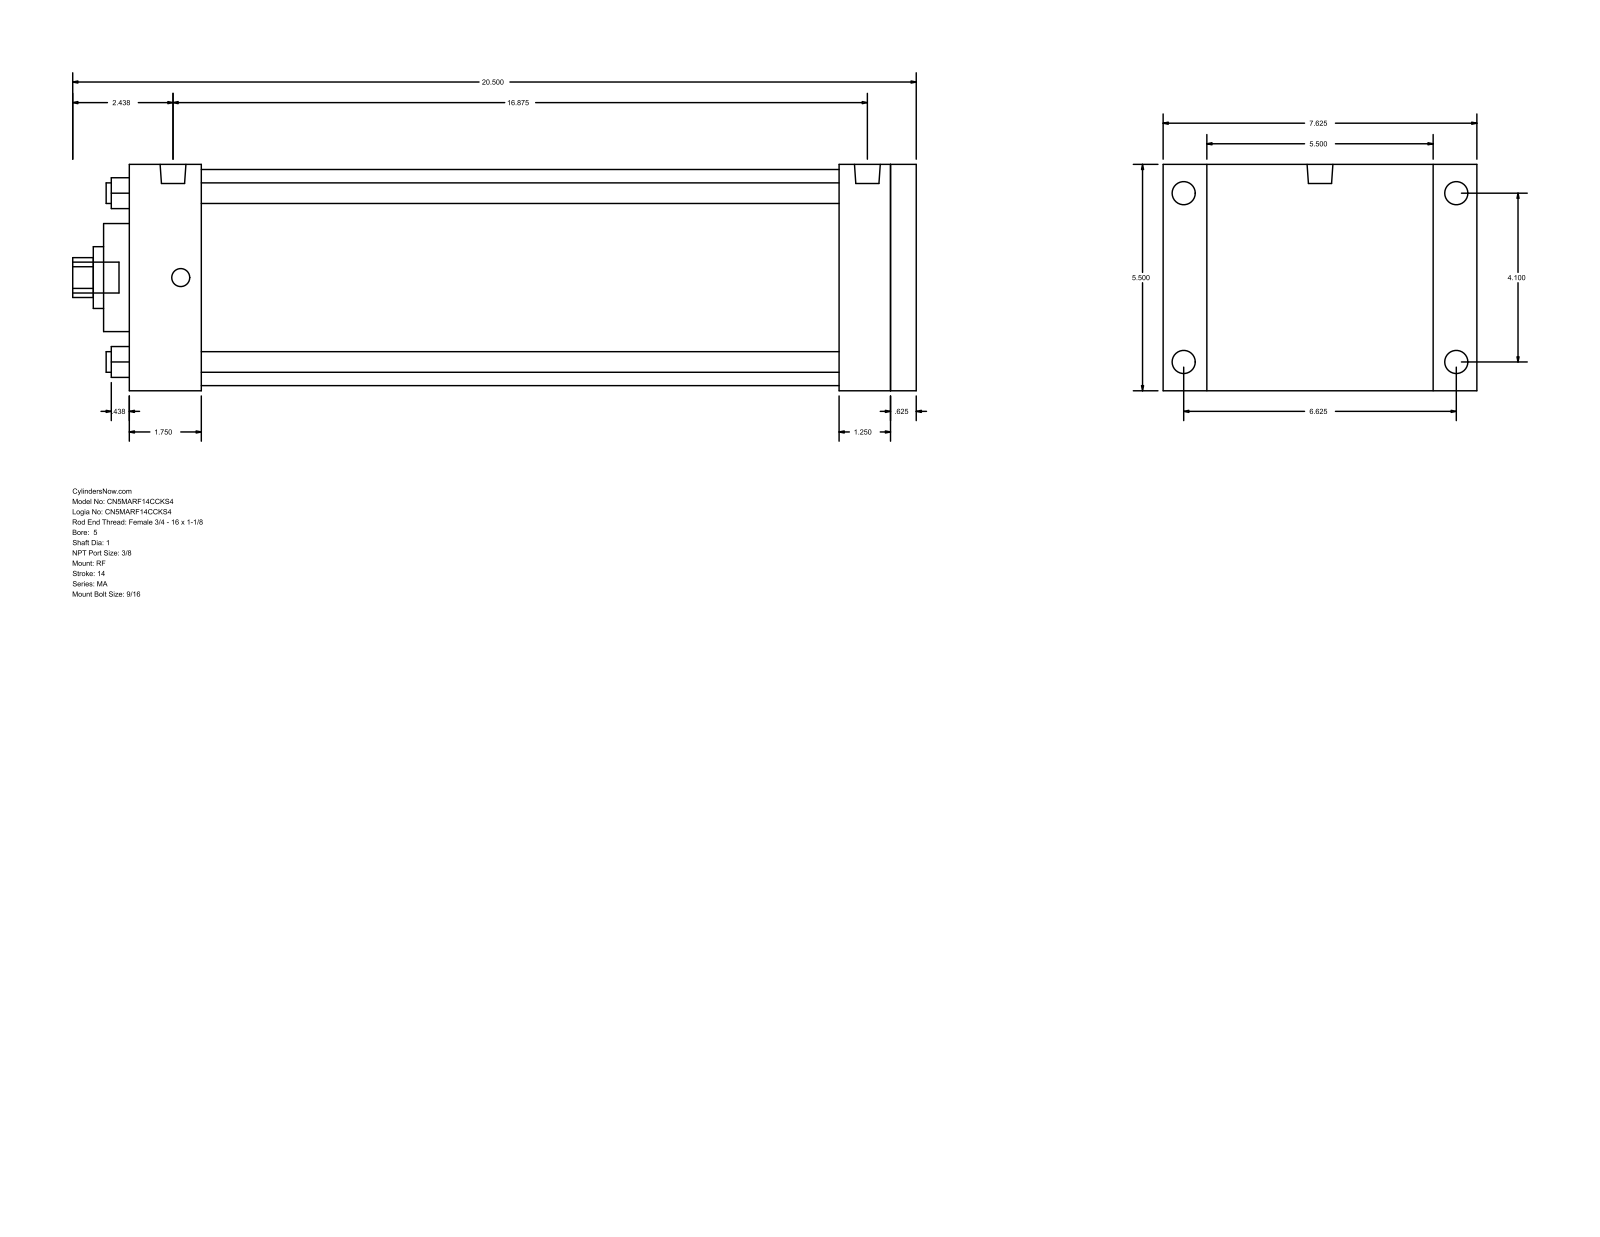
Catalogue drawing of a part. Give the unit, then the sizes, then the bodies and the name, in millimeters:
Units: millimetres
Overall size (bounding box): 520.7 × 193.68 × 139.7
Round holes (diameter × count): ⌀12.7 ×4, ⌀25.4 ×1, ⌀38.1 ×1, ⌀66.67 ×1, ⌀133.35 ×1
Round bosses / shafts (diameter × count): ⌀14.29 ×4, ⌀11.11 ×4, ⌀15.93 ×2, ⌀19.05 ×1
Partial cylindrical surfaces — rounded edges, fillets, slot ends (radius × count): R12.29 ×1
Main face-to-face distances: 139.7, 485.78, 469.9, 15.88, 44.46, 425.44, 441.32, 438.15, 393.69, 31.75
Hole centre spacings: 73.64, 104.14, 147.28
Bodies: 0 solids, 94 faces (65 planar, 29 cylindrical, 0 other)
Part name (STEP PRODUCT): MA_RF__0500_1
STEP written by: GSSL Pune (CONFIG_CONTROL_DESIGN)
